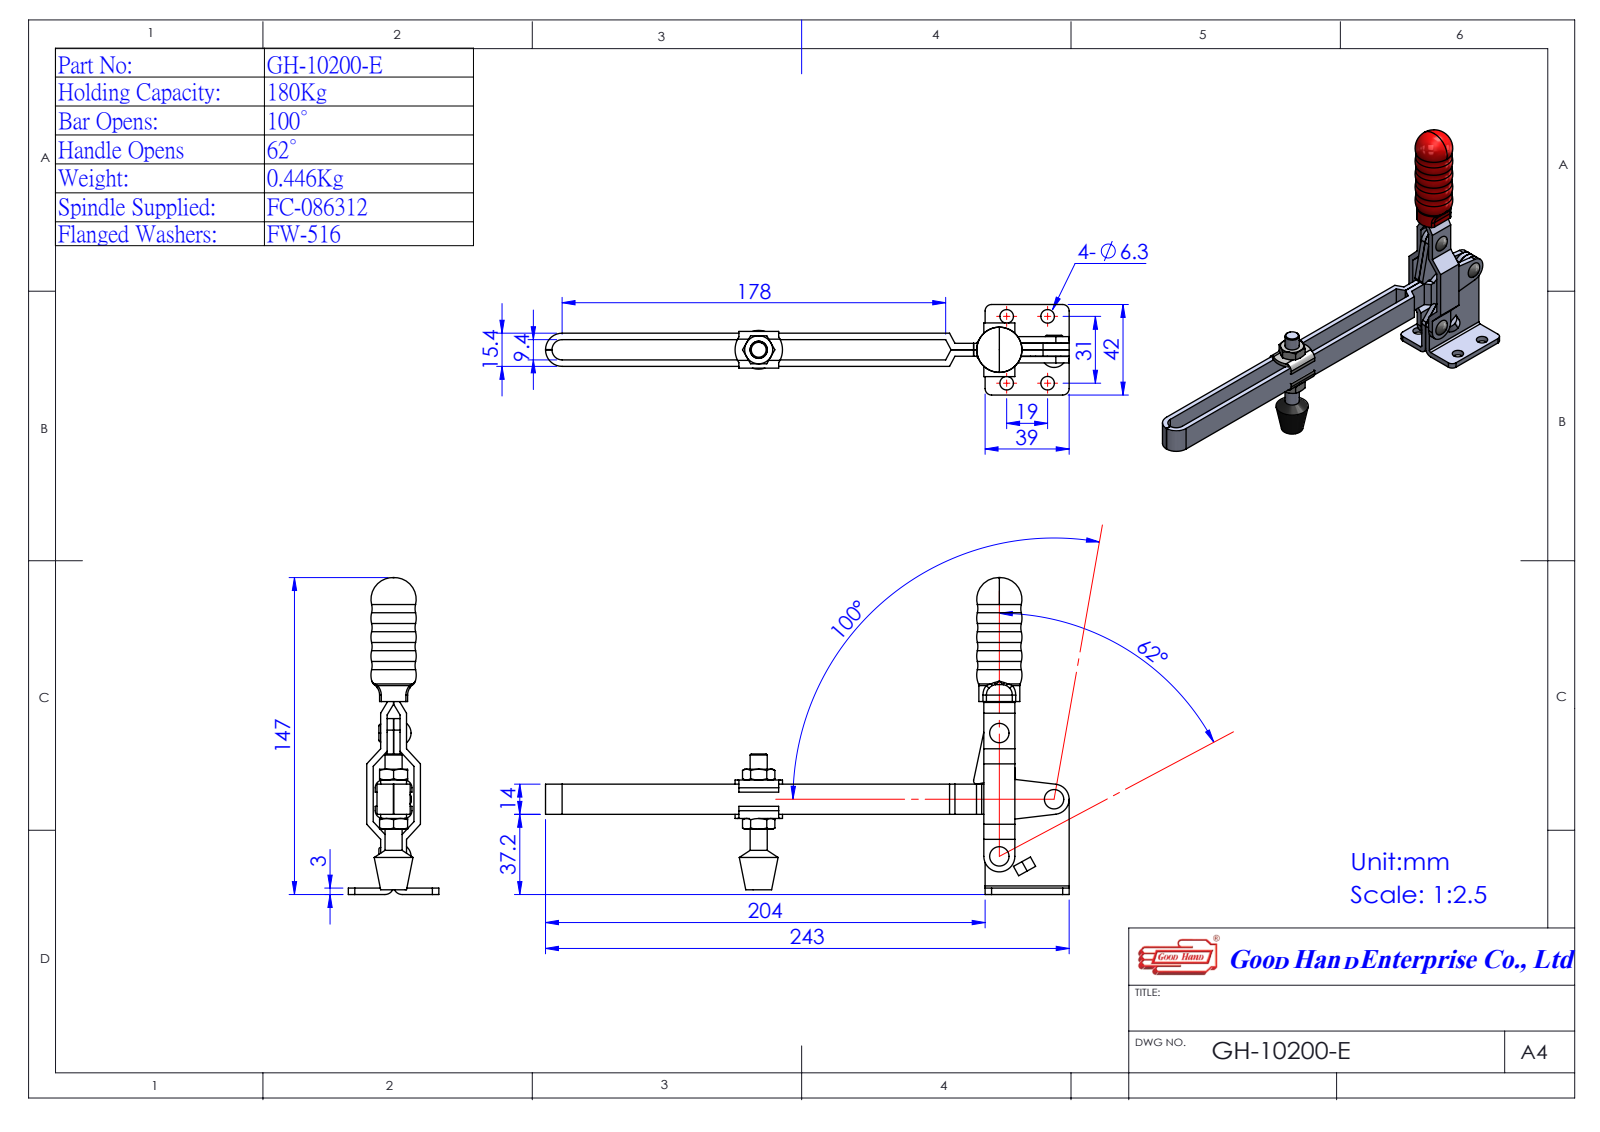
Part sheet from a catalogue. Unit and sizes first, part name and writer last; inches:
Units: inches
Overall size (bounding box): 9.567 × 5.788 × 1.654
Round holes (diameter × count): ⌀0.197 ×4, ⌀0.248 ×4
Round bosses / shafts (diameter × count): ⌀0.248 ×2, ⌀0.312 ×1
Partial cylindrical surfaces — rounded edges, fillets, slot ends (radius × count): R0.118 ×6, R0.047 ×4, R0.079 ×4, R0.142 ×4, R0.157 ×2, R0.236 ×2, R0.266 ×2, R0.435 ×2
Main face-to-face distances: 0.118, 0.185, 0.303, 0.421, 0.067, 0.488, 0.236, 0.606, 0.37, 0.063
Hole centre spacings: 0.748, 1.22, 1.431, 0.953, 1.044, 1.209, 1.445, 1.569
Volume: 4.335 in³ · Surface area: 63.59 in²
Bodies: 5 solids, 320 faces (136 planar, 90 cylindrical, 94 other)
Part name (STEP PRODUCT): 零件46^GH-10200-E(簡化); Group4^GH-101-D(簡化); GH-10200-E(簡化); Group5^GH-10200-E(簡化) (+2 more)
STEP written by: SolidWorks 2016 (AUTOMOTIVE_DESIGN)
